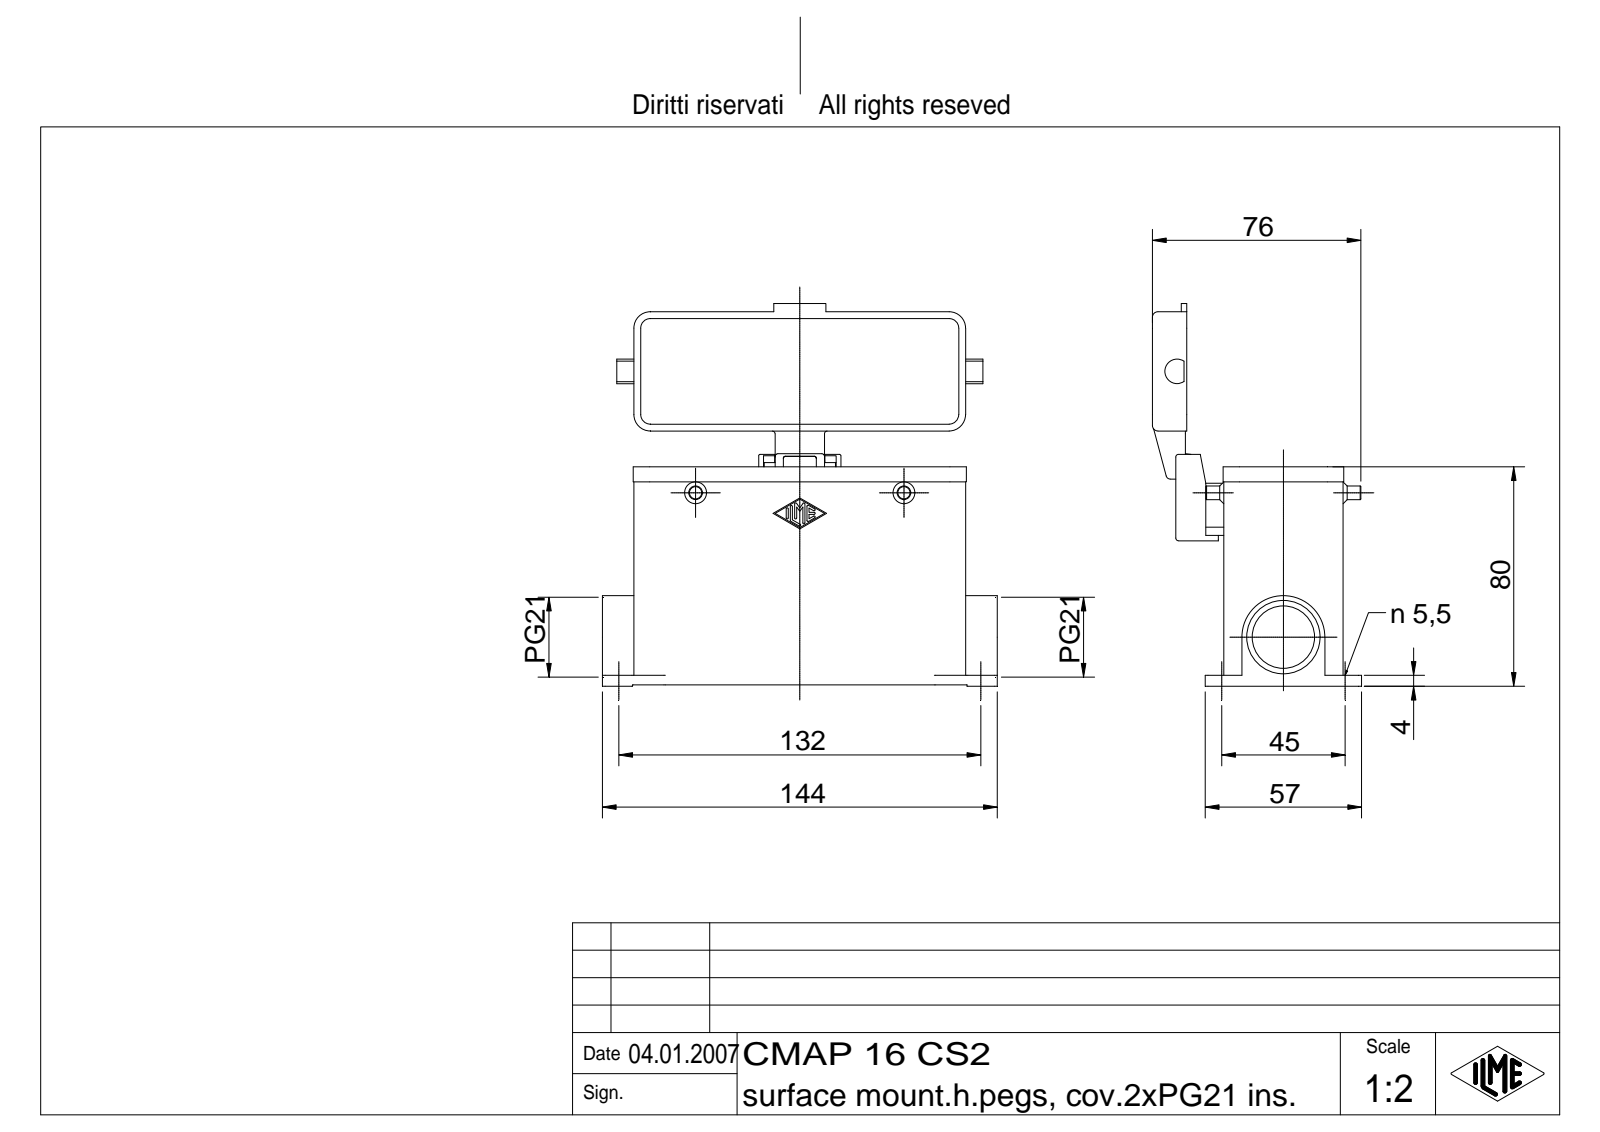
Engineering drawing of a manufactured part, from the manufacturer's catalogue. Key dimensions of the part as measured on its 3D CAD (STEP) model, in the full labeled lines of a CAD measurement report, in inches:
Part name (STEP PRODUCT): CMAP 16 CS2
STEP written by: Autodesk Inventor 7 (AUTOMOTIVE_DESIGN)
Units: inches
Bodies: 2 solids, 474 faces (177 planar, 177 cylindrical, 120 other)
Overall size (bounding box): 5.669 × 5.492 × 3.002
Volume: 9.798 in³ · Surface area: 136.9 in²
Round holes (diameter × count): ⌀0.217 ×4, ⌀0.157 ×1, ⌀0.197 ×1, ⌀0.897 ×1, ⌀1.054 ×1
Round bosses / shafts (diameter × count): ⌀0.197 ×2, ⌀0.118 ×2, ⌀0.276 ×1, ⌀0.157 ×1
Partial cylindrical surfaces — rounded edges, fillets, slot ends (radius × count): R0.039 ×26, R0.015 ×14, R0.236 ×12, R0.02 ×9, R0.028 ×8, R0.079 ×8, R0.118 ×4, R0.138 ×4
Main face-to-face distances: 0.118, 1.594, 1.713, 0.138, 1.476, 2.736, 2.618, 0.886, 1.142, 1.024
Hole centre spacings: 1.772, 5.197, 5.491
